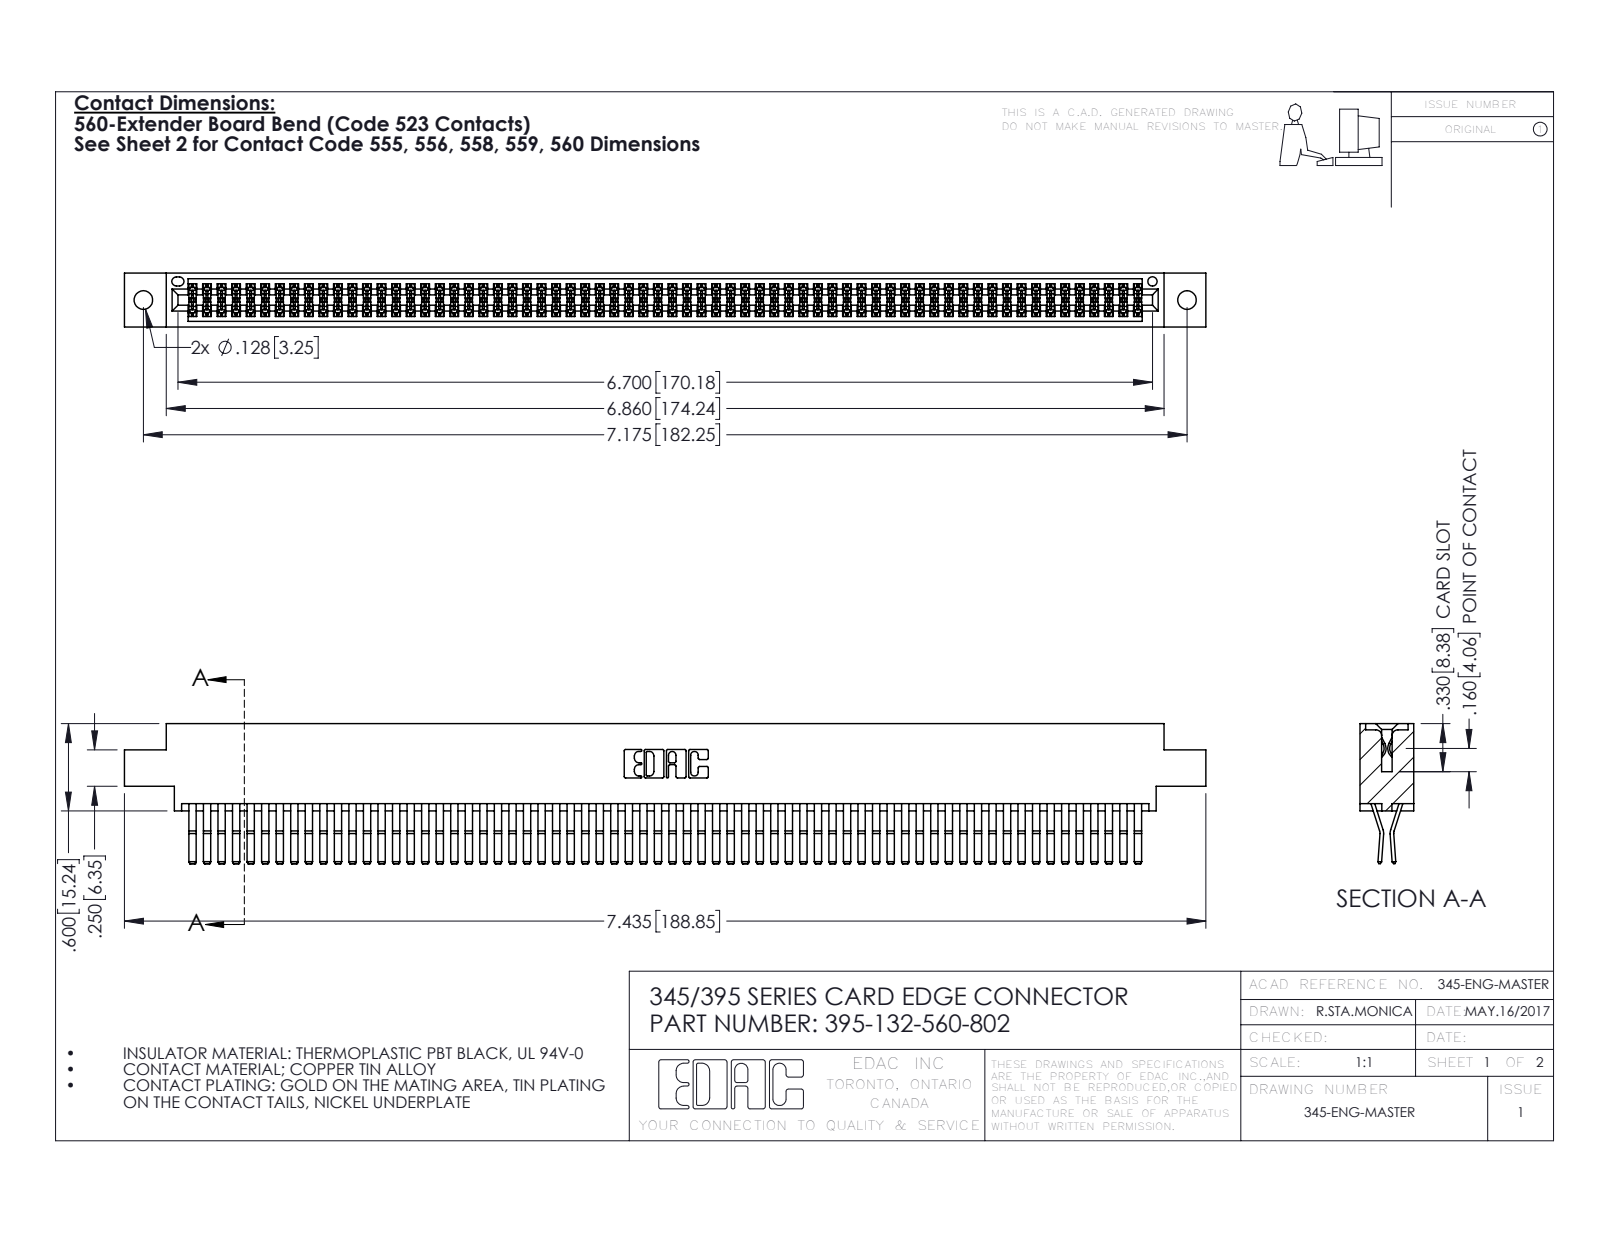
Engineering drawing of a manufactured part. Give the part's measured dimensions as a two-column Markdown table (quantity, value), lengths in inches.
| quantity | value |
| --- | --- |
| part name | 395-132-560-802; 345 Part_0.170 Offset - 0.128 Dia; 345-292-001_560 Tail |
| STEP written by | SolidWorks 2016 (CONFIG_CONTROL_DESIGN) |
| units | inches |
| bodies | 133 solids, 6994 faces (4440 planar, 2554 cylindrical, 0 other) |
| overall size | 7.435 × 0.962 × 0.37 |
| volume | 1.177 in³ |
| surface area | 48.15 in² |
| round holes (diameter × count) | 0.128 × 2, 0.064 × 1 |
| partial cylindrical surfaces (radius × count) | 0.006 × 199, 0.01 × 22, 0.007 × 6, 0.031 × 6, 0.026 × 3, 0.01 × 2, 0.014 × 2, 0.019 × 2 |
| main face-to-face distances | 0.025, 0.298, 0.072, 0.37, 0.2, 0.098, 0.272, 0.225, 0.175, 0.149 |
| hole center spacings | 0.27, 6.939, 7.175 |
